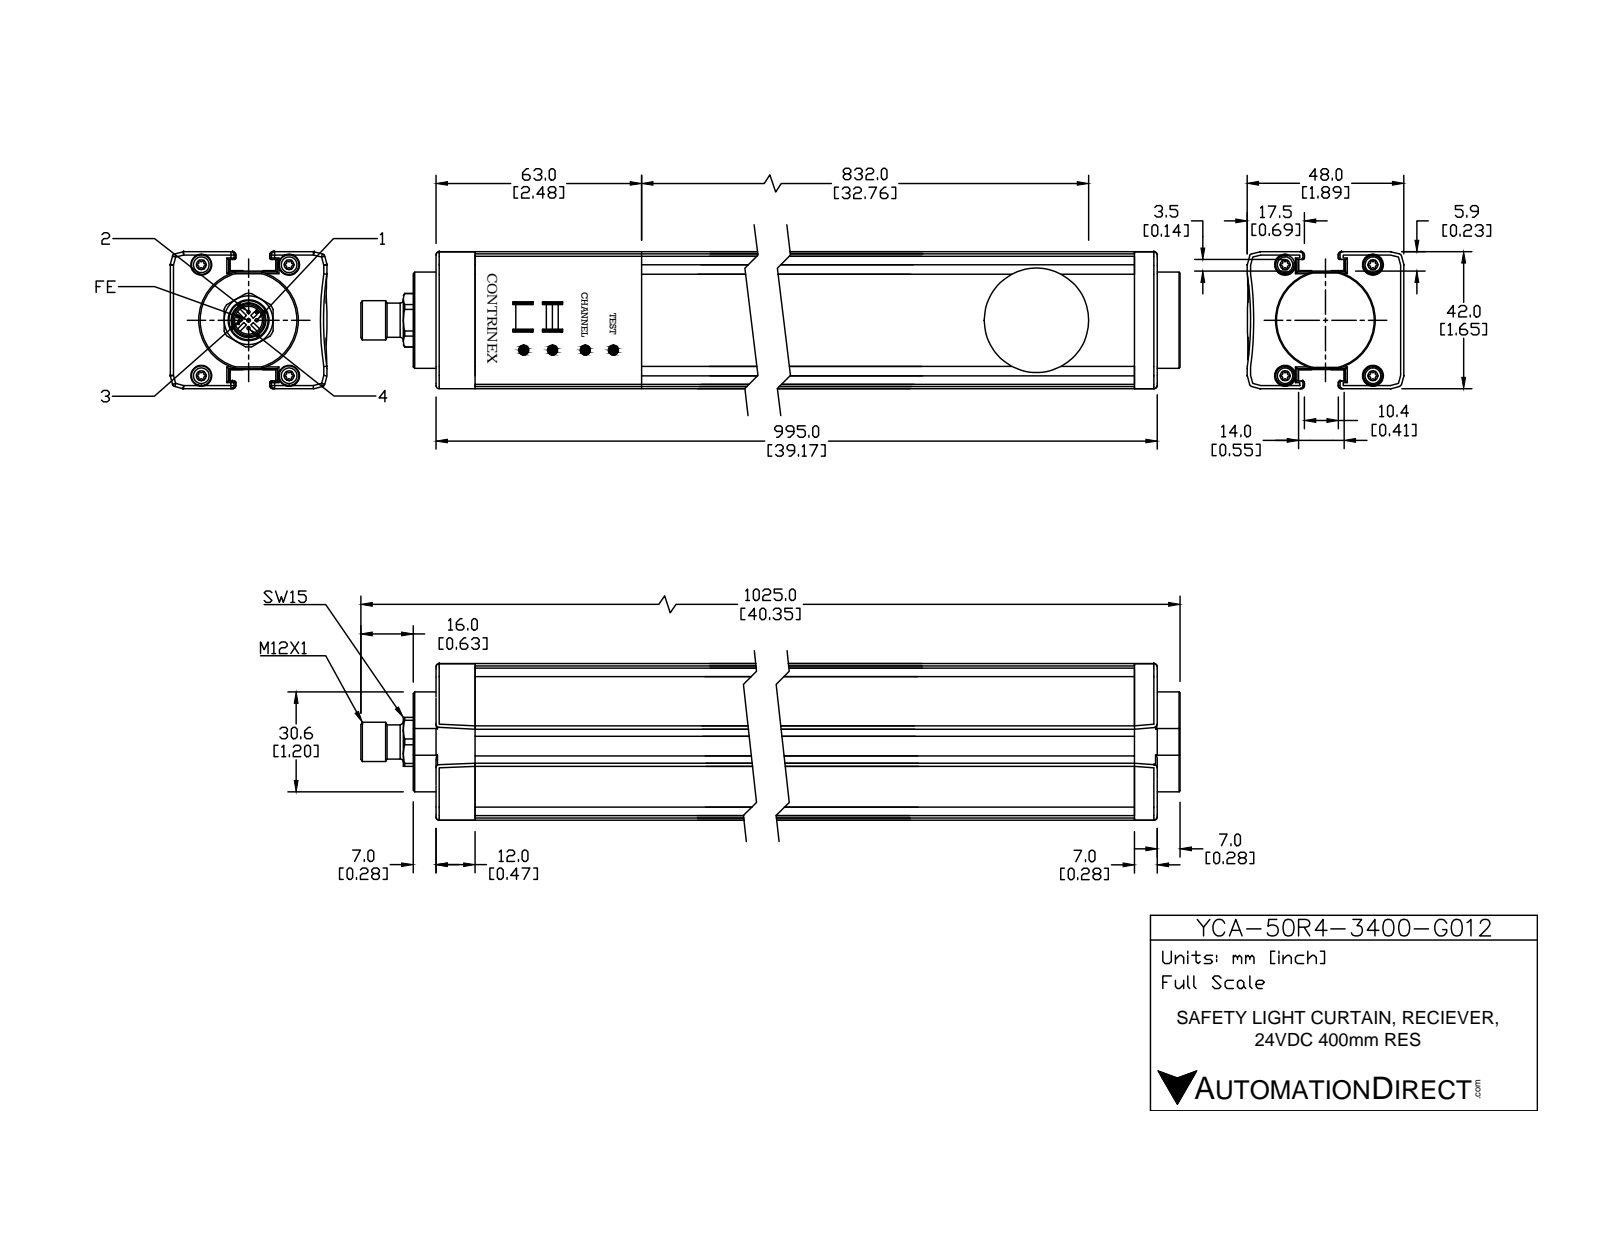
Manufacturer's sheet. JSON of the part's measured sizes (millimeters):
{"part_name": "YCA-50R4-3400-G012", "step_written_by": "SolidWorks 2016 (AUTOMOTIVE_DESIGN)", "units": "millimeters", "bodies": {"solids": 18, "faces": 454, "planar": 221, "cylindrical": 172, "other": 61}, "overall_size": [1025, 48, 42], "volume_mm3": 1794000, "surface_area_mm2": 231840, "round_holes": [[6, 4], [1, 1], [8.5, 1], [32, 1]], "round_bosses_or_shafts": [[5.5, 4], [1, 4], [30.6, 1], [12, 1], [10.5, 1]], "partial_cylinders_radius": [[1, 52], [0.5, 4], [8.2, 1], [100, 1]], "face_to_face_distances": [42, 5.8, 36.2, 29.4, 1, 6.8, 35.2, 30.4, 14, 17.2], "hole_center_spacings": [21.04, 22.34, 26.9, 34, 43.35]}
